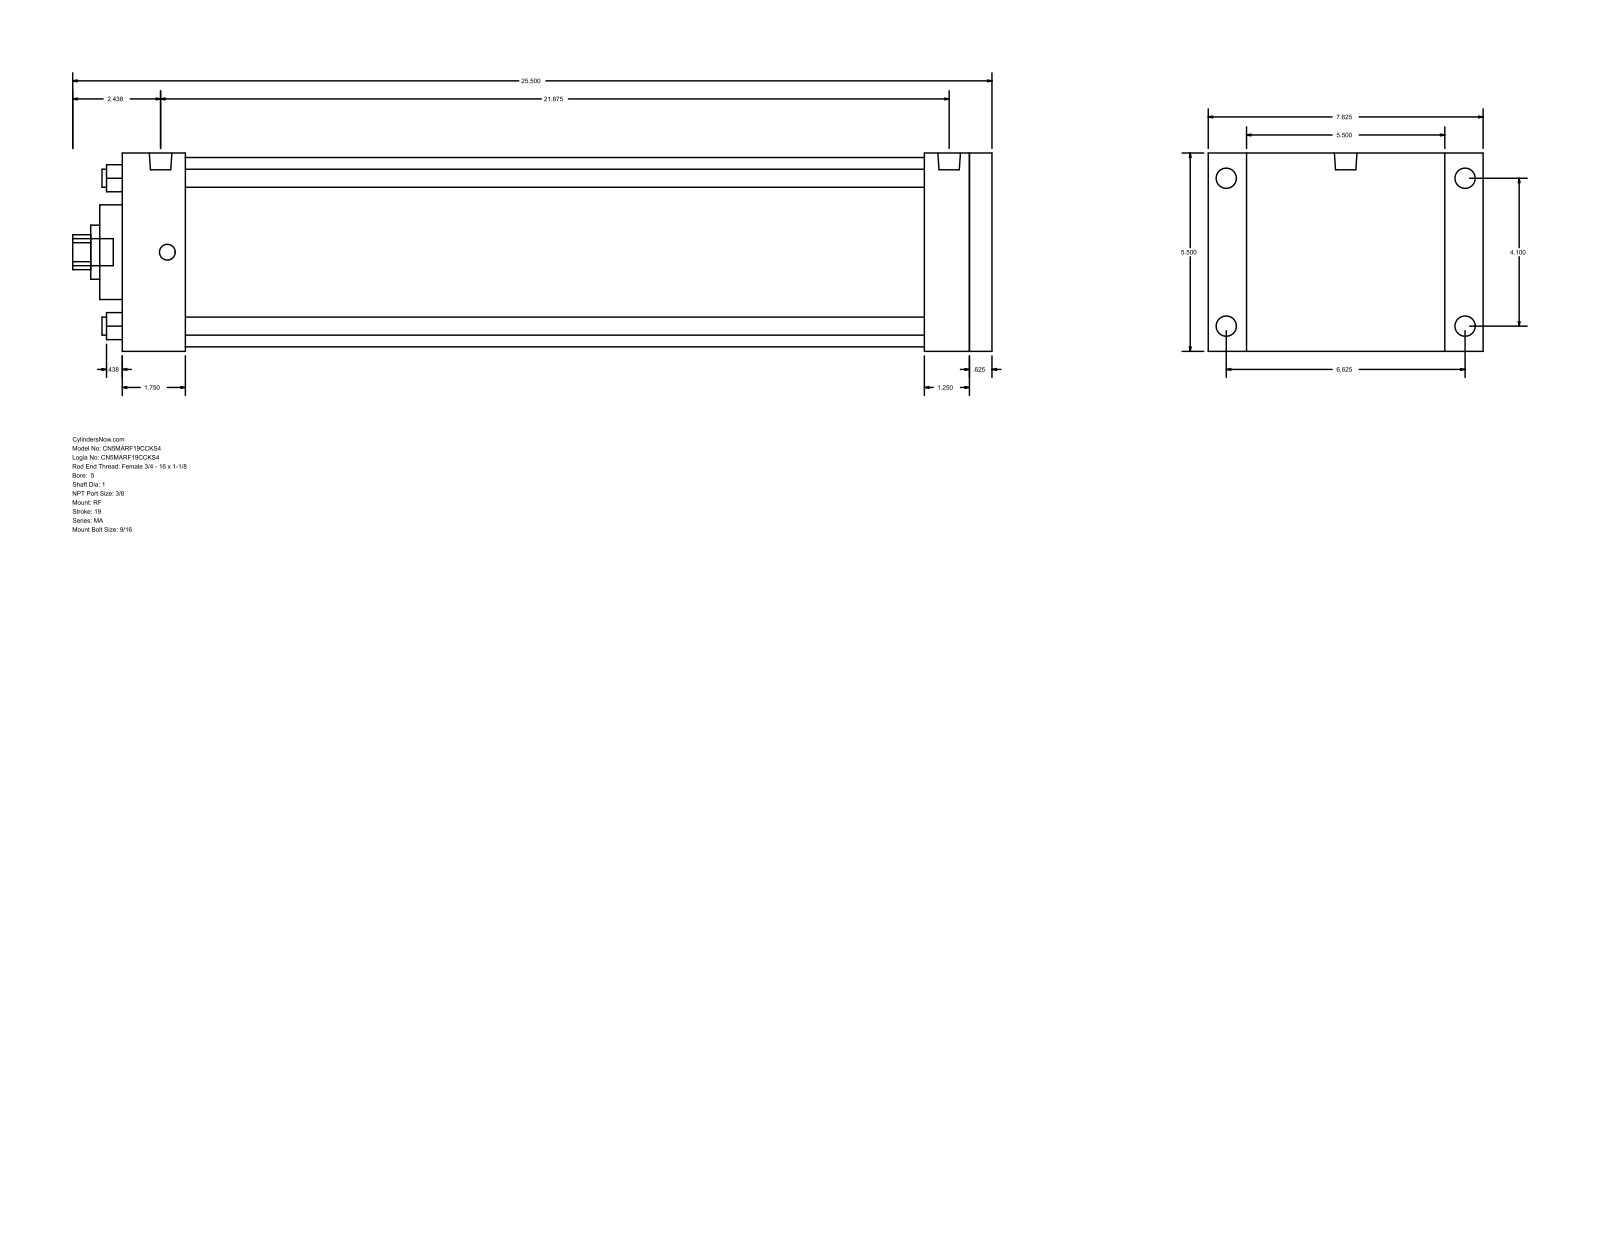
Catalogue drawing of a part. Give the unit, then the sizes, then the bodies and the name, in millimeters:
Units: millimetres
Overall size (bounding box): 647.7 × 193.68 × 139.7
Round holes (diameter × count): ⌀12.7 ×4, ⌀25.4 ×1, ⌀38.1 ×1, ⌀66.67 ×1, ⌀133.35 ×1
Round bosses / shafts (diameter × count): ⌀14.29 ×4, ⌀11.11 ×4, ⌀15.93 ×2, ⌀19.05 ×1
Partial cylindrical surfaces — rounded edges, fillets, slot ends (radius × count): R12.29 ×1
Main face-to-face distances: 139.7, 612.78, 15.87, 596.91, 44.46, 552.45, 568.32, 565.16, 520.7, 31.75
Hole centre spacings: 73.64, 104.14, 147.28
Bodies: 0 solids, 94 faces (65 planar, 29 cylindrical, 0 other)
Part name (STEP PRODUCT): MA_RF__0500_1
STEP written by: GSSL Pune (CONFIG_CONTROL_DESIGN)
